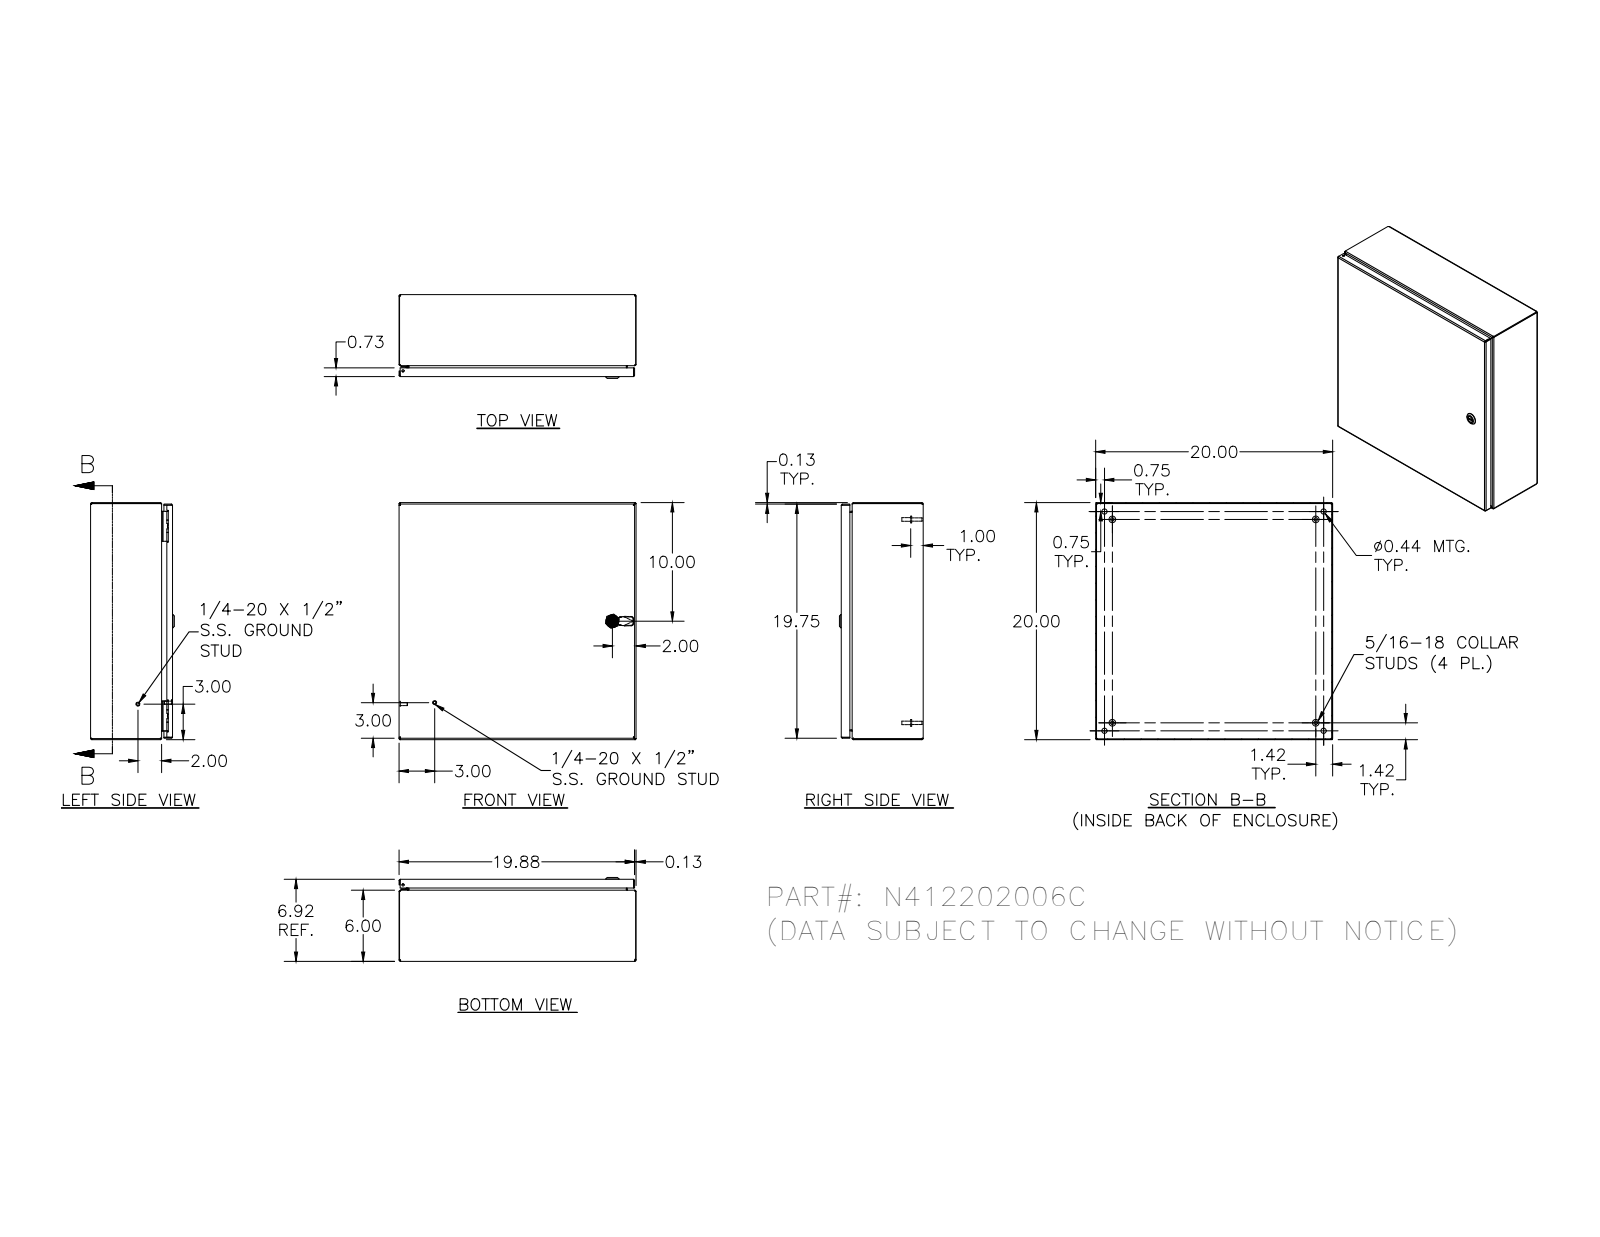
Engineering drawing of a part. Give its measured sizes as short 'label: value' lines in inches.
name: N412202006C
written by: SolidWorks 2018 (AUTOMOTIVE_DESIGN)
unit: in
bodies: 33 solids, 1449 faces (530 planar, 547 cylindrical, 372 other)
size: 20 × 20 × 7.075
volume: 106.8 in³; area: 2 906 in²
holes: 5× ⌀0.188, 4× ⌀0.093, 4× ⌀0.152, 4× ⌀0.167, 4× ⌀0.172, 4× ⌀0.437, 2× ⌀0.156, 1× ⌀0.187, 1× ⌀0.197, 1× ⌀0.315, 1× ⌀0.394, 1× ⌀0.402
bosses: 10× ⌀0.25, 4× ⌀0.563, 4× ⌀0.36, 4× ⌀0.32, 4× ⌀0.3, 4× ⌀0.275, 4× ⌀0.256, 4× ⌀0.164
rounds: 30× R0.012, 30× R0.031, 26× R0.05, 20× R0.105, 18× R0.016, 16× R0.125, 13× R0.02, 8× R0.032
face distances: 0.074, 6.843, 6.769, 6.917, 19.926, 19.852, 0.074, 19.926, 20, 0.917
hole spacings: 16, 0.66, 0.656, 1.307, 1.965, 15.34, 16.66, 18.5
